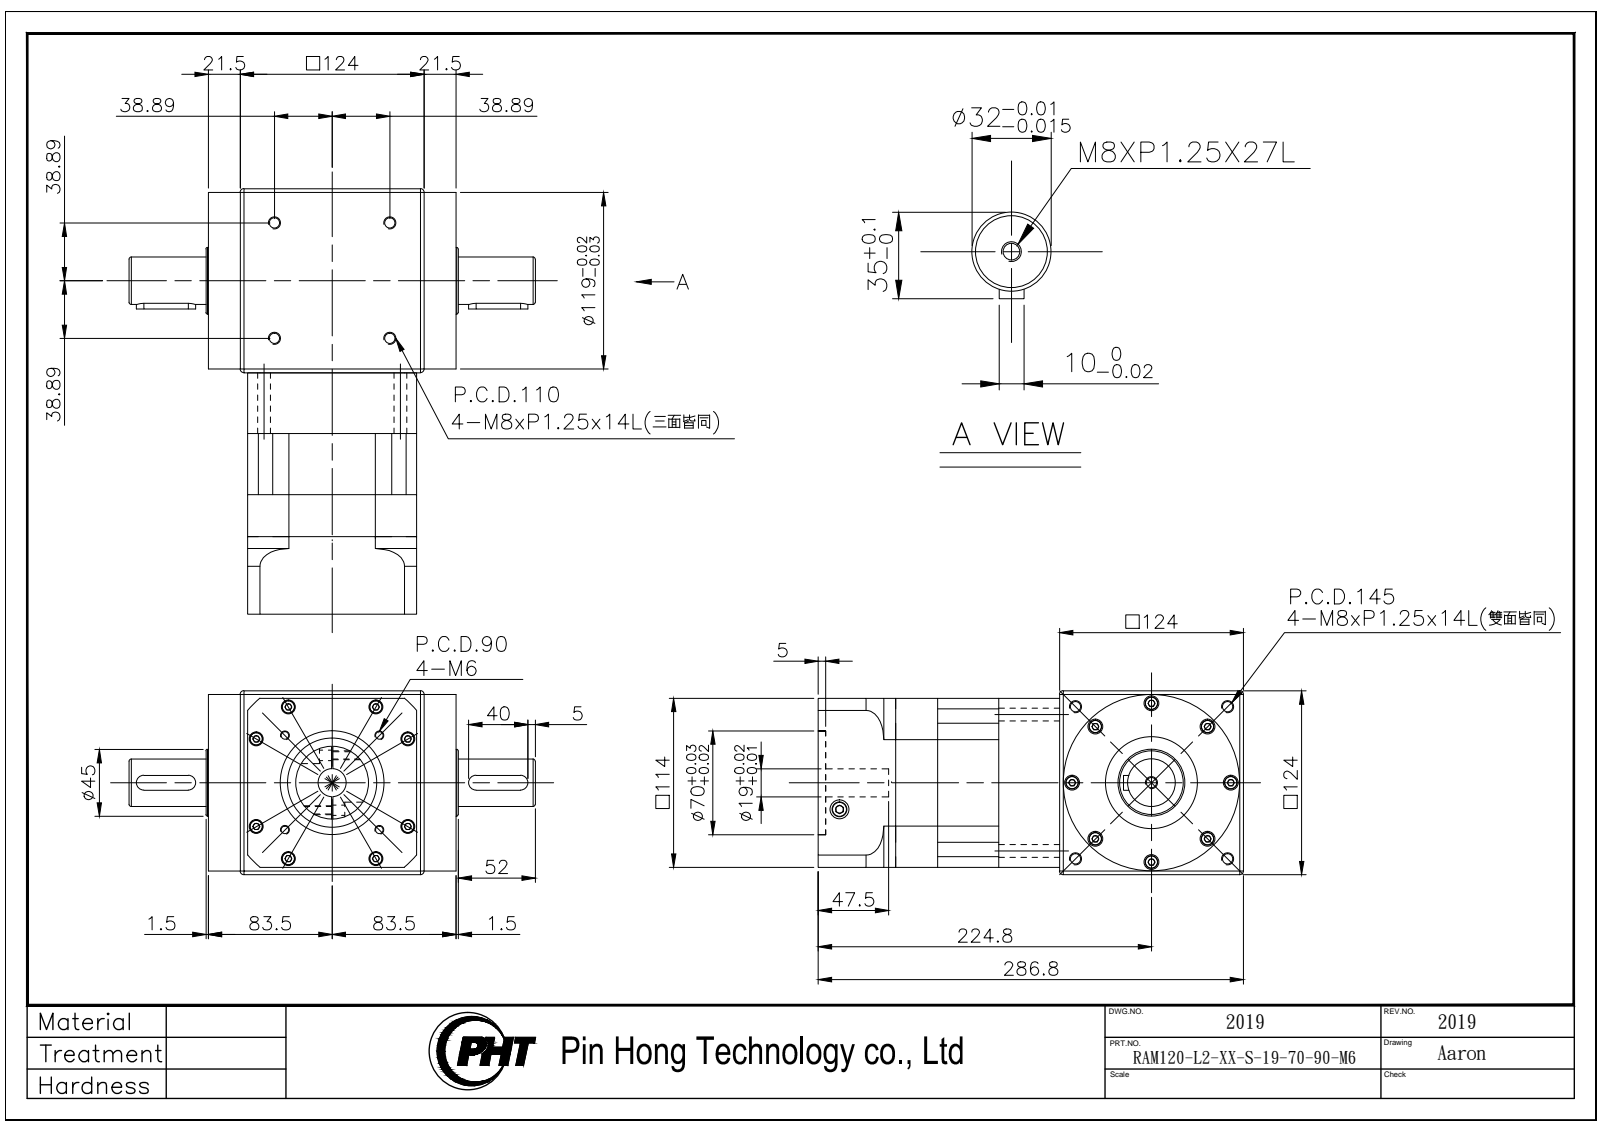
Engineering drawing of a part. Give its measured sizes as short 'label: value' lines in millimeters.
name: RAM120-L2-XX-2S-19-70-90-M6_2019
written by: SolidWorks 2016 (AUTOMOTIVE_DESIGN)
unit: mm
bodies: 7 solids, 889 faces (437 planar, 288 cylindrical, 164 other)
size: 286.8 × 274 × 124
volume: 4 342 000 mm³; area: 357 699 mm²
holes: 13× ⌀6.8, 8× ⌀5.3, 8× ⌀9, 8× ⌀9.5, 8× ⌀14, 4× ⌀5, 4× ⌀8.6, 2× ⌀12.7, 1× ⌀4.08, 1× ⌀19, 1× ⌀60, 1× ⌀70
bosses: 12× ⌀13, 8× ⌀8.5, 1× ⌀119, 1× ⌀110, 1× ⌀62, 1× ⌀49, 1× ⌀45, 1× ⌀32
rounds: 4× R5, 4× R7, 1× R64, 1× R75, 1× R86.2
face distances: 5, 119, 124, 114, 69.5, 28.3, 41.2, 41, 110.5, 82.2
hole spacings: 59, 10, 15.4, 17.24, 19.42, 39.8, 51.28, 52
